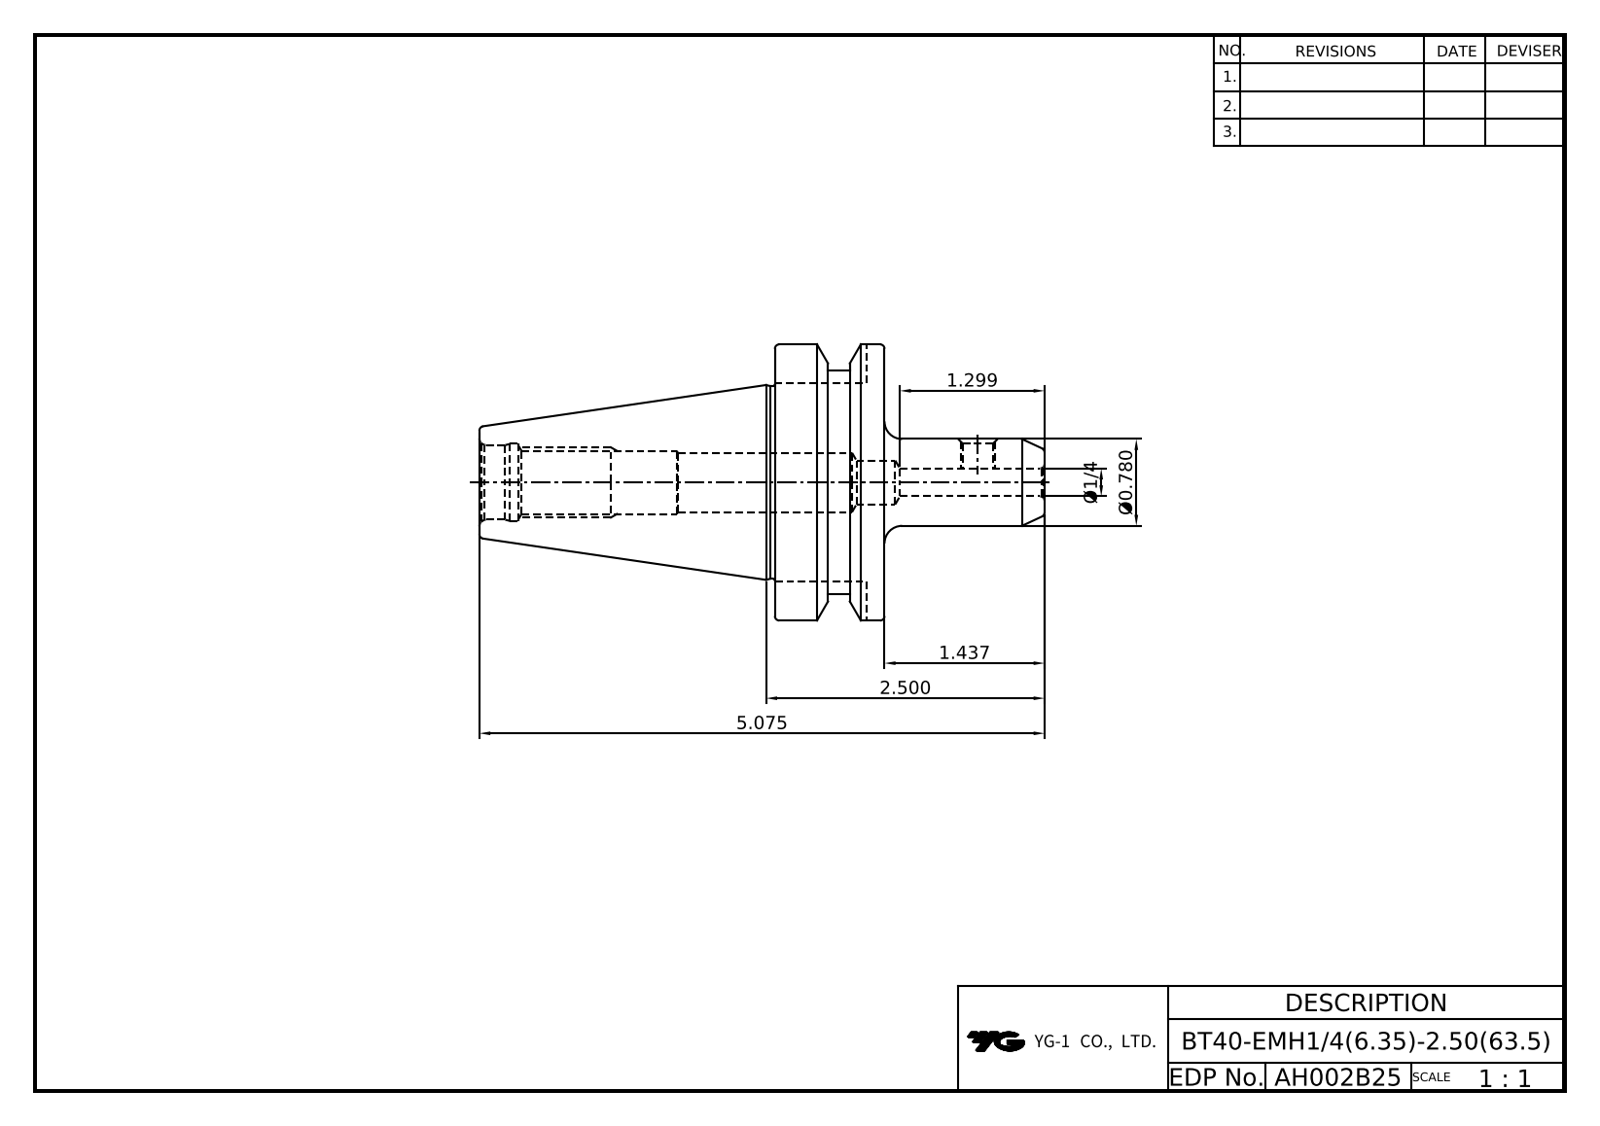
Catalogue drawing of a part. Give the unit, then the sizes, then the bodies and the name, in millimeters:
Units: millimetres
Overall size (bounding box): 128.9 × 63 × 63
Round holes (diameter × count): ⌀5.36 ×1, ⌀6.35 ×1, ⌀10 ×1, ⌀13.5 ×1, ⌀13.84 ×1, ⌀17 ×1, ⌀17.6 ×1
Round bosses / shafts (diameter × count): ⌀63 ×1, ⌀52.6 ×1, ⌀44 ×1, ⌀19.81 ×1
Partial cylindrical surfaces — rounded edges, fillets, slot ends (radius × count): R8.05 ×1
Main face-to-face distances: 25, 45.2, 16.1, 67.4, 92.4, 128.9, 61.5, 36.5, 84.5, 17.1
Volume: 129 896 mm³ · Surface area: 25 367 mm²
Bodies: 1 solid, 51 faces (15 planar, 16 cylindrical, 20 other)
Part name (STEP PRODUCT): LO-BT40-EMH6.35-63.5
STEP written by: Autodesk Inventor 2022 (AUTOMOTIVE_DESIGN)
